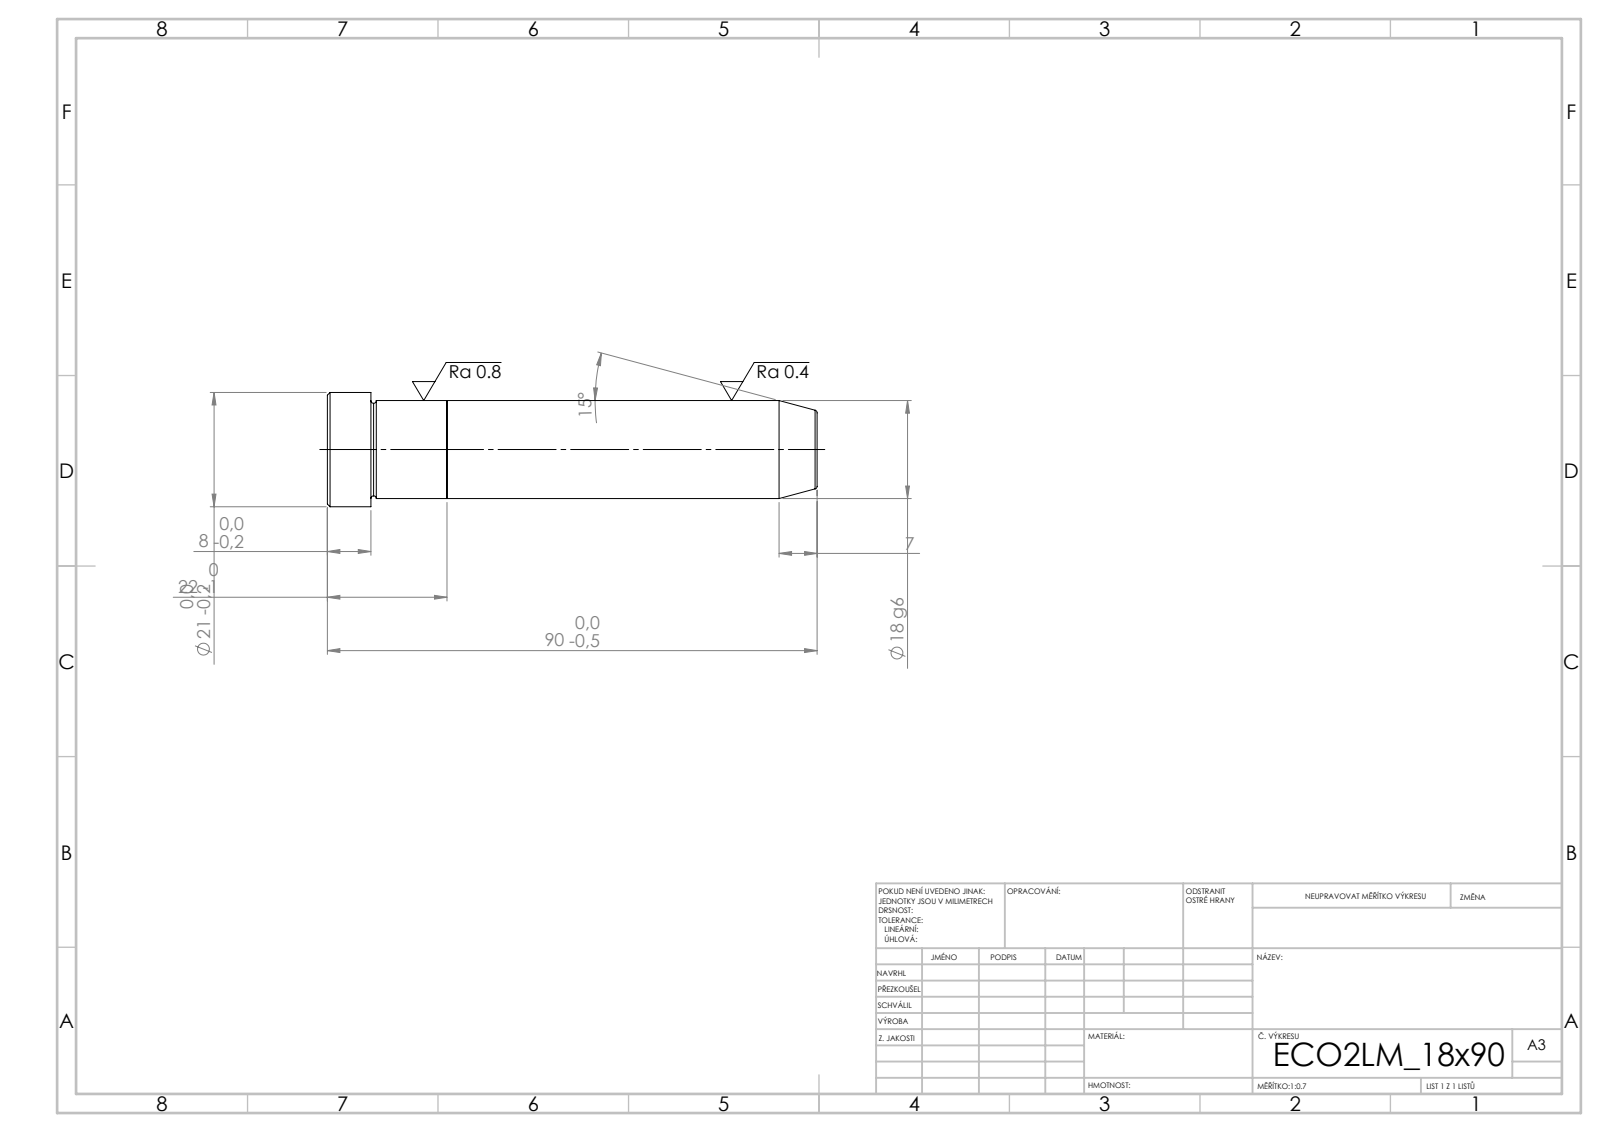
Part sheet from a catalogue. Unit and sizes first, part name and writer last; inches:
Units: inches
Overall size (bounding box): 3.543 × 0.827 × 0.827
Round bosses / shafts (diameter × count): ⌀0.827 ×1, ⌀0.709 ×1
Main face-to-face distances: 0.866, 2.677, 3.543, 3.228, 0.551, 0.315
Volume: 1.419 in³ · Surface area: 9.683 in²
Bodies: 2 solids, 21 faces (5 planar, 6 cylindrical, 10 other)
STEP written by: SolidWorks 2019 (CONFIG_CONTROL_DESIGN)
